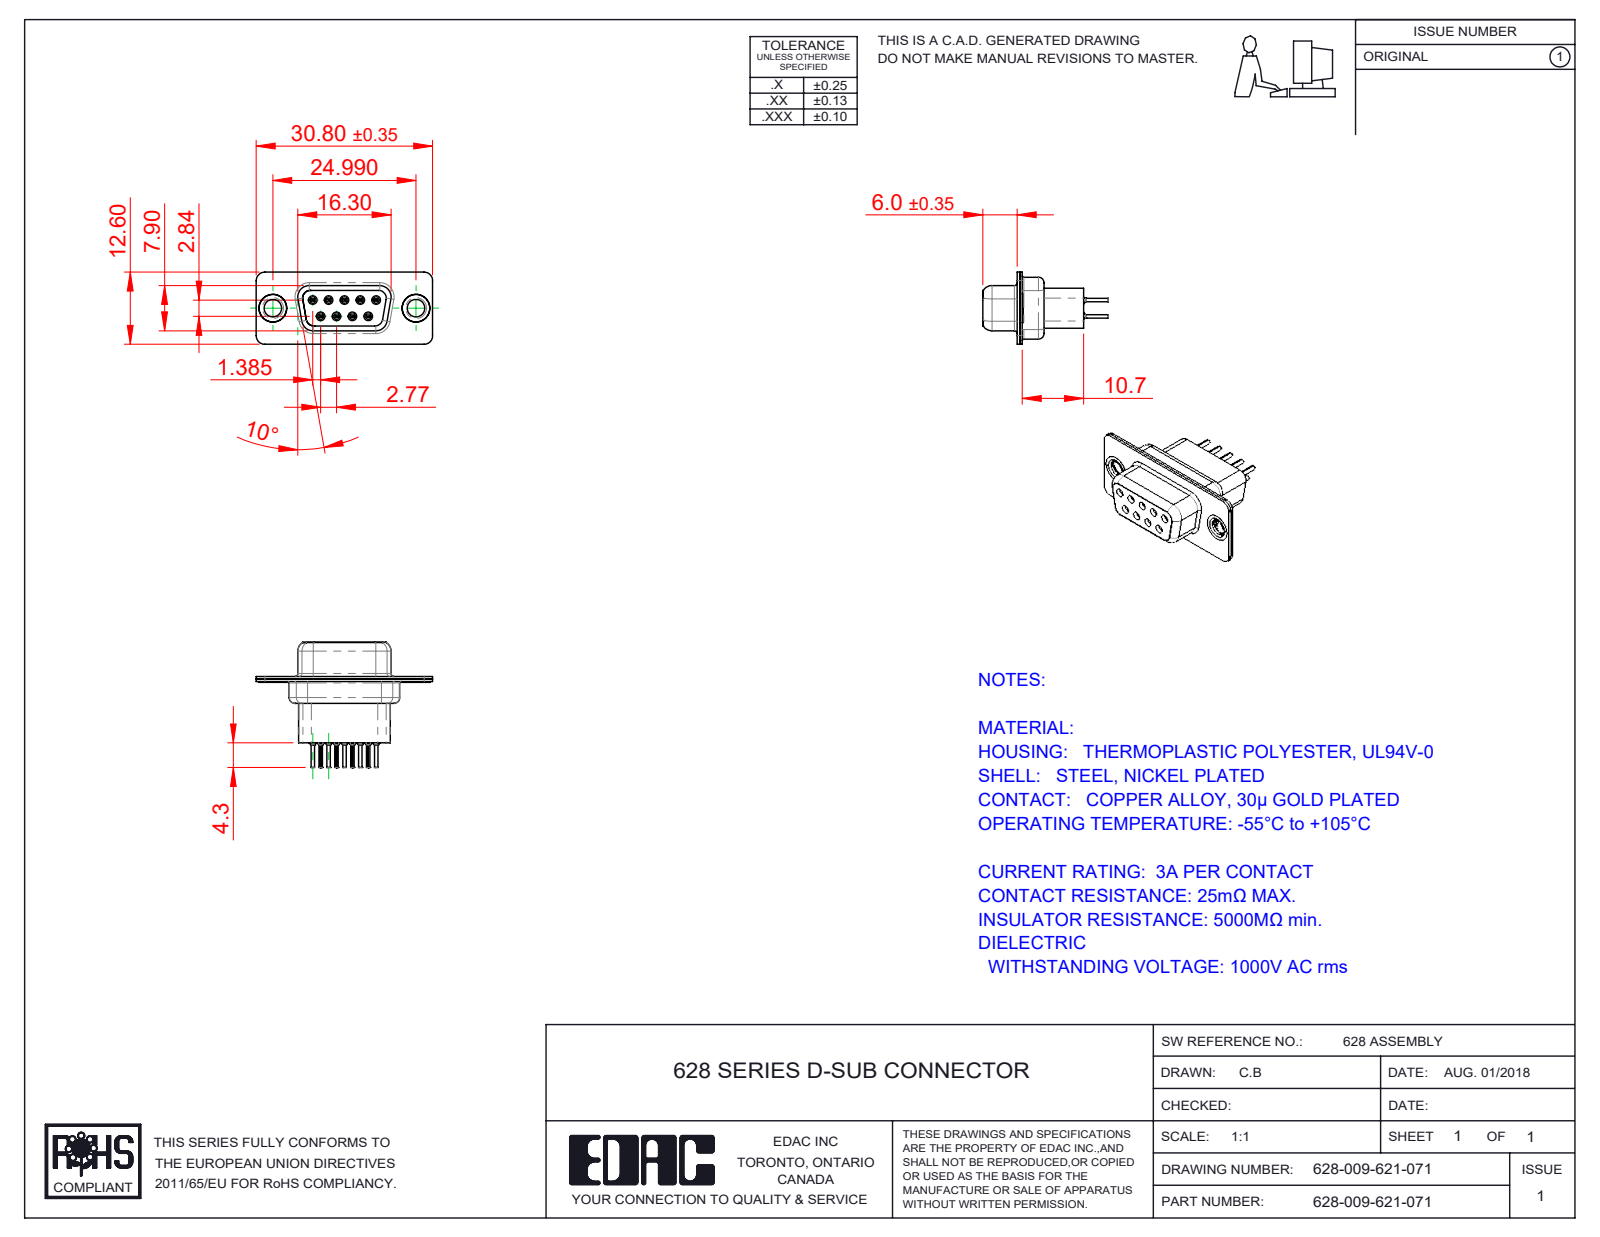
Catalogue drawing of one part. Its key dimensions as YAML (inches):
part_name: "628 Shell Rear_09 Contacts; 628 Contact Row 2_21H; 628 Housing_09 HP; 628-009-621-071 (+3 more)"
step_written_by: "SolidWorks 2020 (CONFIG_CONTROL_DESIGN)"
units: inches
bodies: {solids: 14, faces: 1360, planar: 346, cylindrical: 418, other: 596}
overall_size: [1.213, 0.862, 0.496]
volume: 0.131
surface_area: 8.045
round_holes:
  - {diameter: 0.008, count: 9}
  - {diameter: 0.031, count: 9}
  - {diameter: 0.035, count: 9}
  - {diameter: 0.043, count: 9}
  - {diameter: 0.063, count: 9}
  - {diameter: 0.067, count: 5}
  - {diameter: 0.12, count: 2}
  - {diameter: 0.157, count: 2}
  - {diameter: 0.159, count: 2}
  - {diameter: 0.191, count: 2}
round_bosses_or_shafts:
  - {diameter: 0.079, count: 9}
  - {diameter: 0.059, count: 9}
  - {diameter: 0.047, count: 9}
  - {diameter: 0.024, count: 9}
  - {diameter: 0.197, count: 2}
  - {diameter: 0.195, count: 2}
  - {diameter: 0.189, count: 2}
  - {diameter: 0.14, count: 2}
partial_cylinders:
  - {radius: 0.004, count: 18}
  - {radius: 0.059, count: 17}
  - {radius: 0.079, count: 12}
  - {radius: 0.011, count: 9}
  - {radius: 0.053, count: 6}
  - {radius: 0.01, count: 4}
  - {radius: 0.02, count: 4}
  - {radius: 0.024, count: 4}
face_to_face_distances: [0.018, 0.016, 0.035, 0.335, 0.26, 0.075, 0.055, 0.276, 0.278, 0.02]
hole_center_spacings: [0.124, 0.109, 0.218, 0.198, 0.198, 0.327, 0.294, 0.295]
